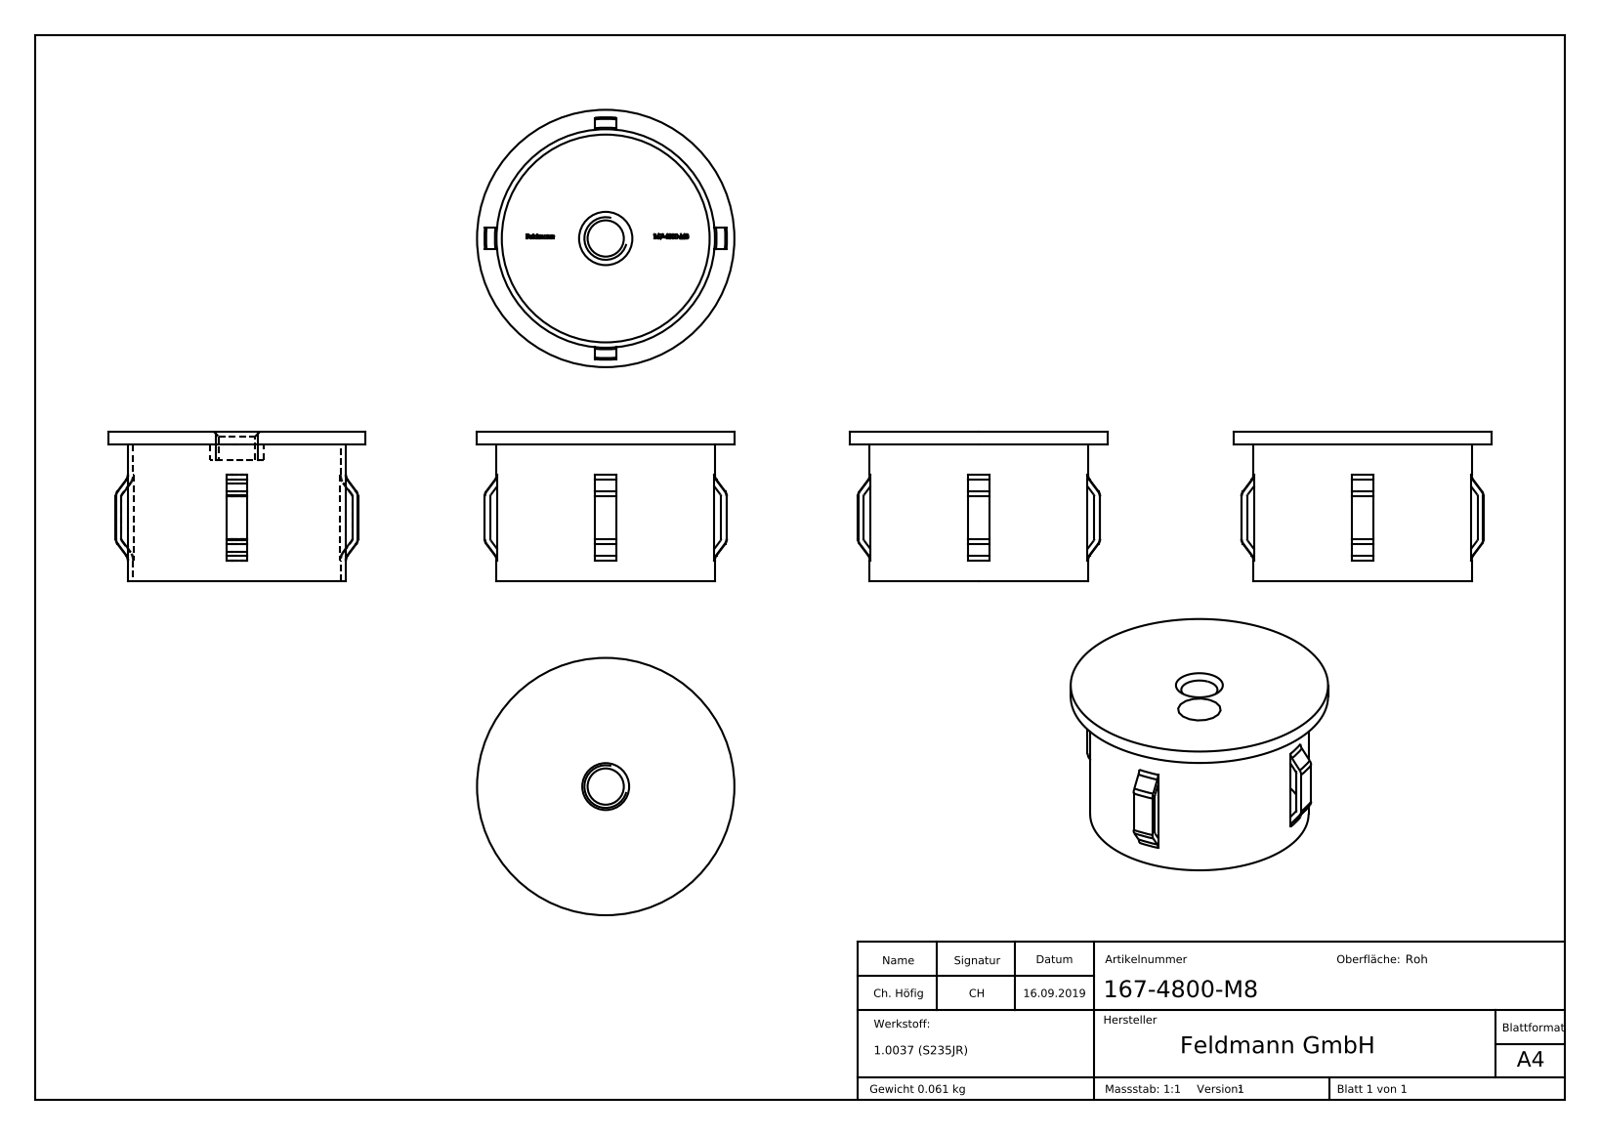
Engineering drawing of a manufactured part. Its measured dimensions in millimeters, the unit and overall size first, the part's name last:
Units: millimetres
Overall size (bounding box): 48.3 × 48.3 × 28.2
Round holes (diameter × count): ⌀6.8 ×1, ⌀39 ×1
Round bosses / shafts (diameter × count): ⌀48.3 ×1, ⌀41 ×1, ⌀10 ×1
Partial cylindrical surfaces — rounded edges, fillets, slot ends (radius × count): R21.75 ×1, R22.75 ×1
Main face-to-face distances: 2.5, 25.7, 28.2, 4, 22.9, 2.8, 5.3, 2.4, 25.8, 2.9
Volume: 7 847 mm³ · Surface area: 10 892 mm²
Bodies: 1 solid, 345 faces (154 planar, 20 cylindrical, 171 other)
Part name (STEP PRODUCT): 167-4800-M8
STEP written by: SolidWorks 2015 (CONFIG_CONTROL_DESIGN)
